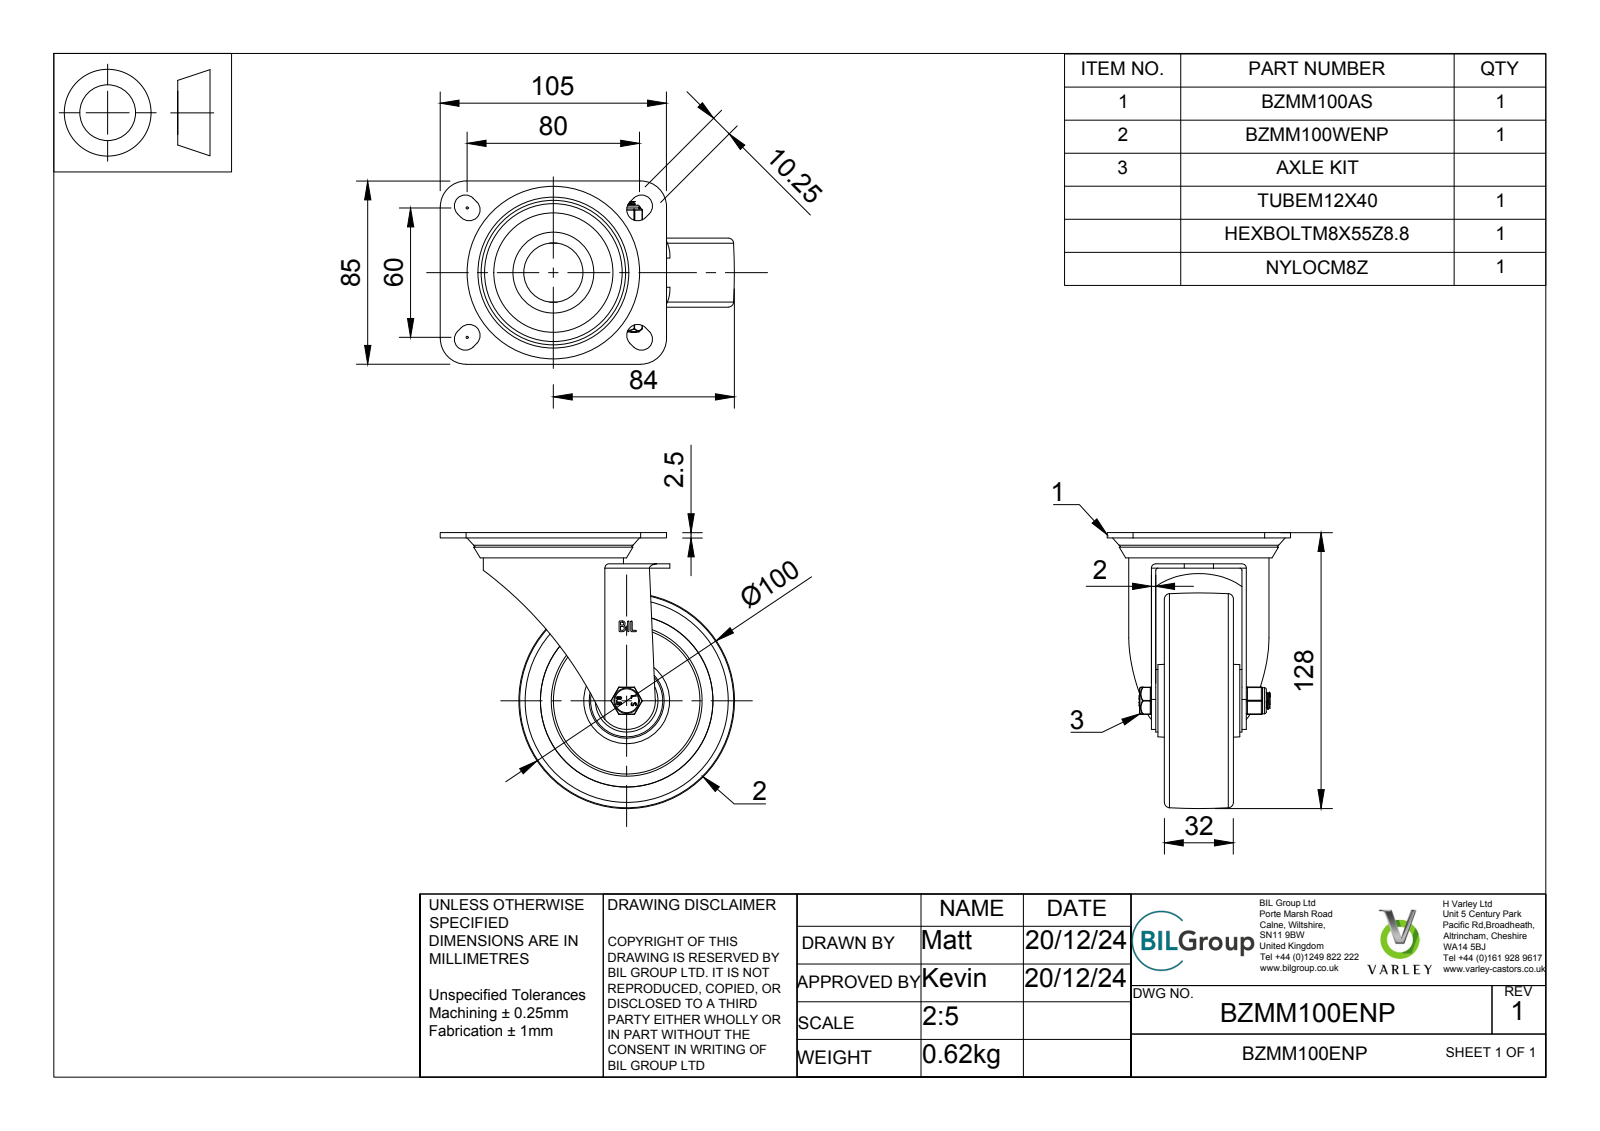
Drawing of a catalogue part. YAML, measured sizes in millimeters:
part_name: "BZMM100ENP v3; BZMM100AS - 2 v2; ZINC PLATED, PRESSED STEEL TOP PLATE; ZINC PLATED, PRESSED STEEL TOP PLATE Geometry (+7 more)"
step_written_by: "Autodesk Translation Framework v13.20.0.188 (AP242_MANAGED_MODEL_BASED_3D_ENGINEERING_MIM_LF)"
units: millimeters
bodies: {solids: 33, faces: 380, planar: 123, cylindrical: 137, other: 120}
overall_size: [136.5, 128, 85]
volume: 231967
surface_area: 108359
round_holes:
  - {diameter: 0.66, count: 2}
  - {diameter: 8, count: 1}
  - {diameter: 8.25, count: 1}
  - {diameter: 8.4, count: 1}
  - {diameter: 8.6, count: 1}
  - {diameter: 12.5, count: 1}
  - {diameter: 27.5, count: 1}
  - {diameter: 48, count: 1}
  - {diameter: 61, count: 1}
  - {diameter: 70, count: 1}
  - {diameter: 80, count: 1}
round_bosses_or_shafts:
  - {diameter: 65, count: 1}
  - {diameter: 31.5, count: 1}
  - {diameter: 29, count: 1}
  - {diameter: 12.1, count: 1}
  - {diameter: 11.9, count: 1}
  - {diameter: 11.5, count: 1}
  - {diameter: 7.87, count: 1}
  - {diameter: 6.45, count: 1}
partial_cylinders:
  - {radius: 0.5, count: 18}
  - {radius: 0.25, count: 12}
  - {radius: 5.12, count: 8}
  - {radius: 0.33, count: 4}
  - {radius: 0.64, count: 4}
  - {radius: 1, count: 4}
  - {radius: 12, count: 4}
  - {radius: 0.63, count: 2}
face_to_face_distances: [2, 13.5, 18.5, 22.5, 4, 17.5, 36, 2.5, 38, 6]
hole_center_spacings: [3.22, 2.49]
